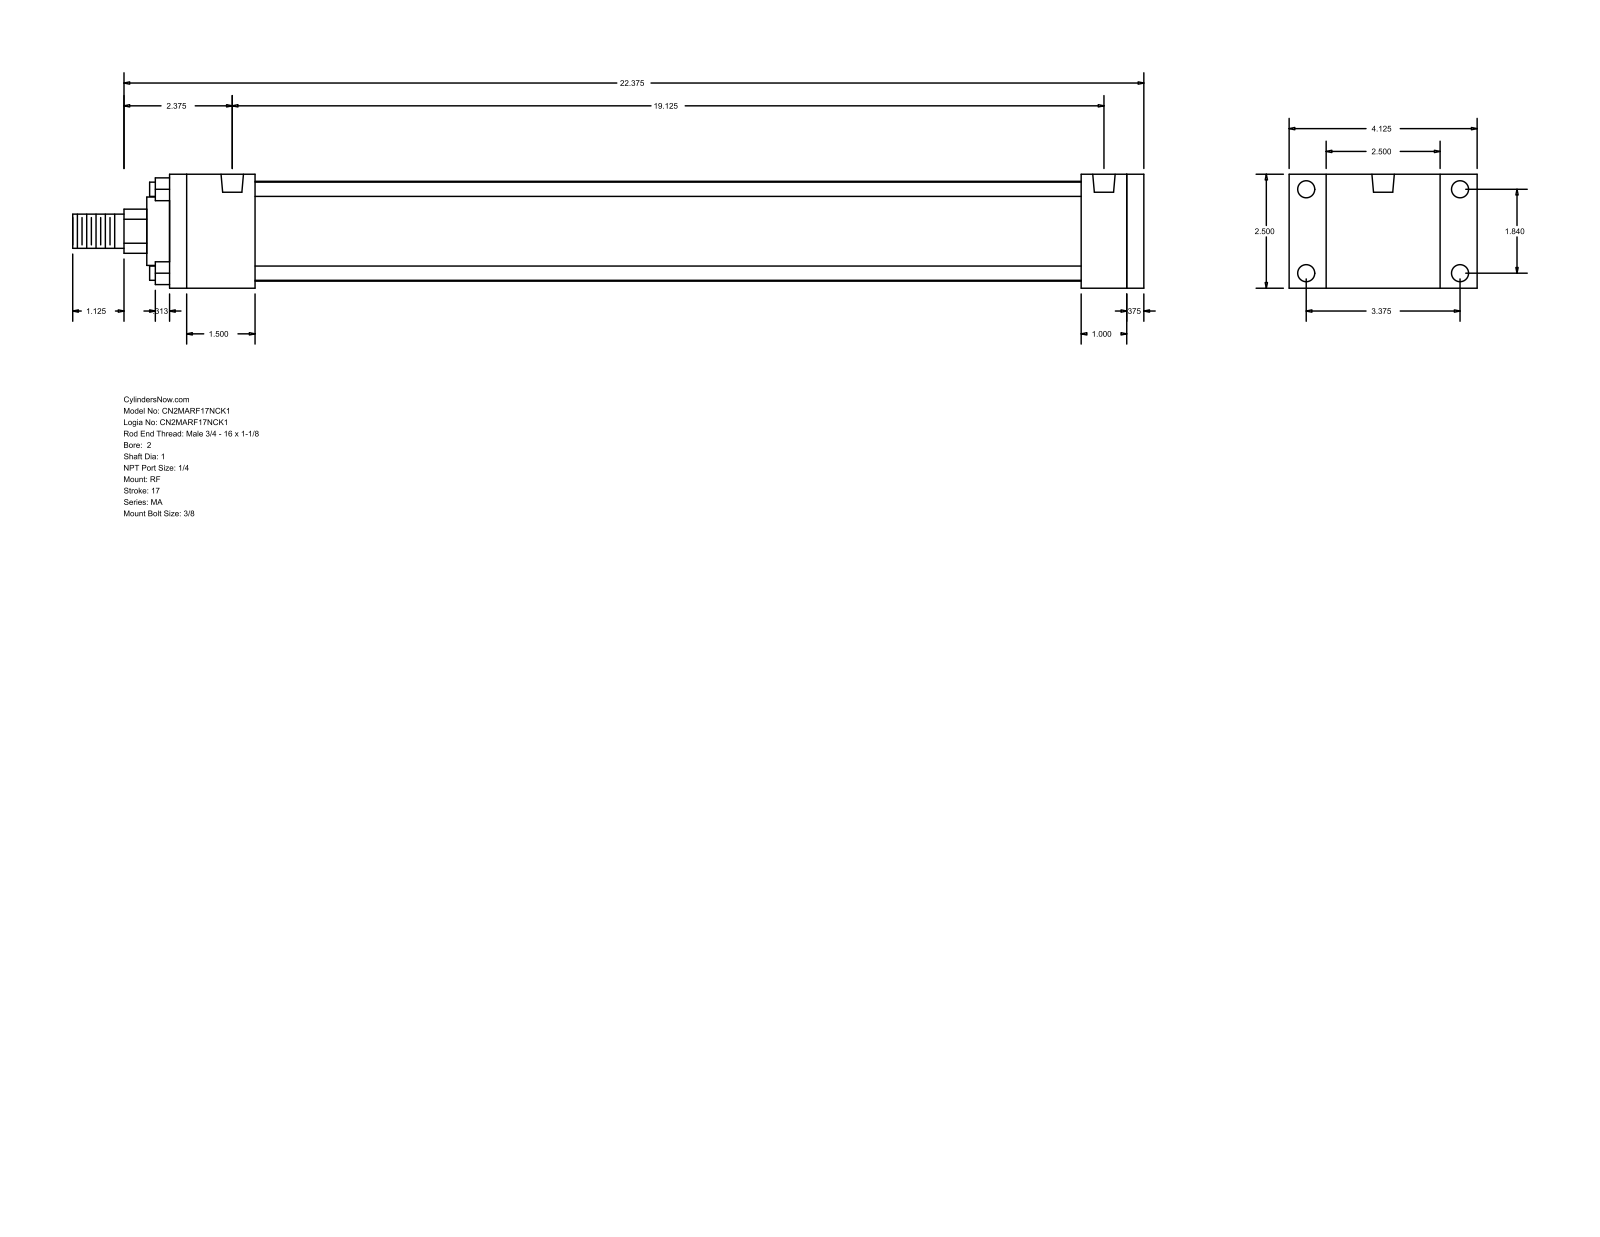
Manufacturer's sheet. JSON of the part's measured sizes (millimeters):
{"part_name": "MA_RF__0200_1", "step_written_by": "GSSL Pune (CONFIG_CONTROL_DESIGN)", "units": "millimeters", "bodies": {"solids": 0, "faces": 92, "planar": 64, "cylindrical": 28, "other": 0}, "overall_size": [596.9, 104.78, 63.5], "round_holes": [[7.94, 4], [9.53, 4], [12.49, 2]], "round_bosses_or_shafts": [[7.94, 4], [55.63, 1], [38.1, 1], [25.4, 1], [19.05, 1]], "partial_cylinders_radius": [[12.29, 1]], "face_to_face_distances": [63.5, 533.4, 9.53, 542.93, 25.4, 20.64, 12.7, 47.63, 485.77, 495.3], "hole_center_spacings": [46.74, 85.72, 97.63, 485.77]}
